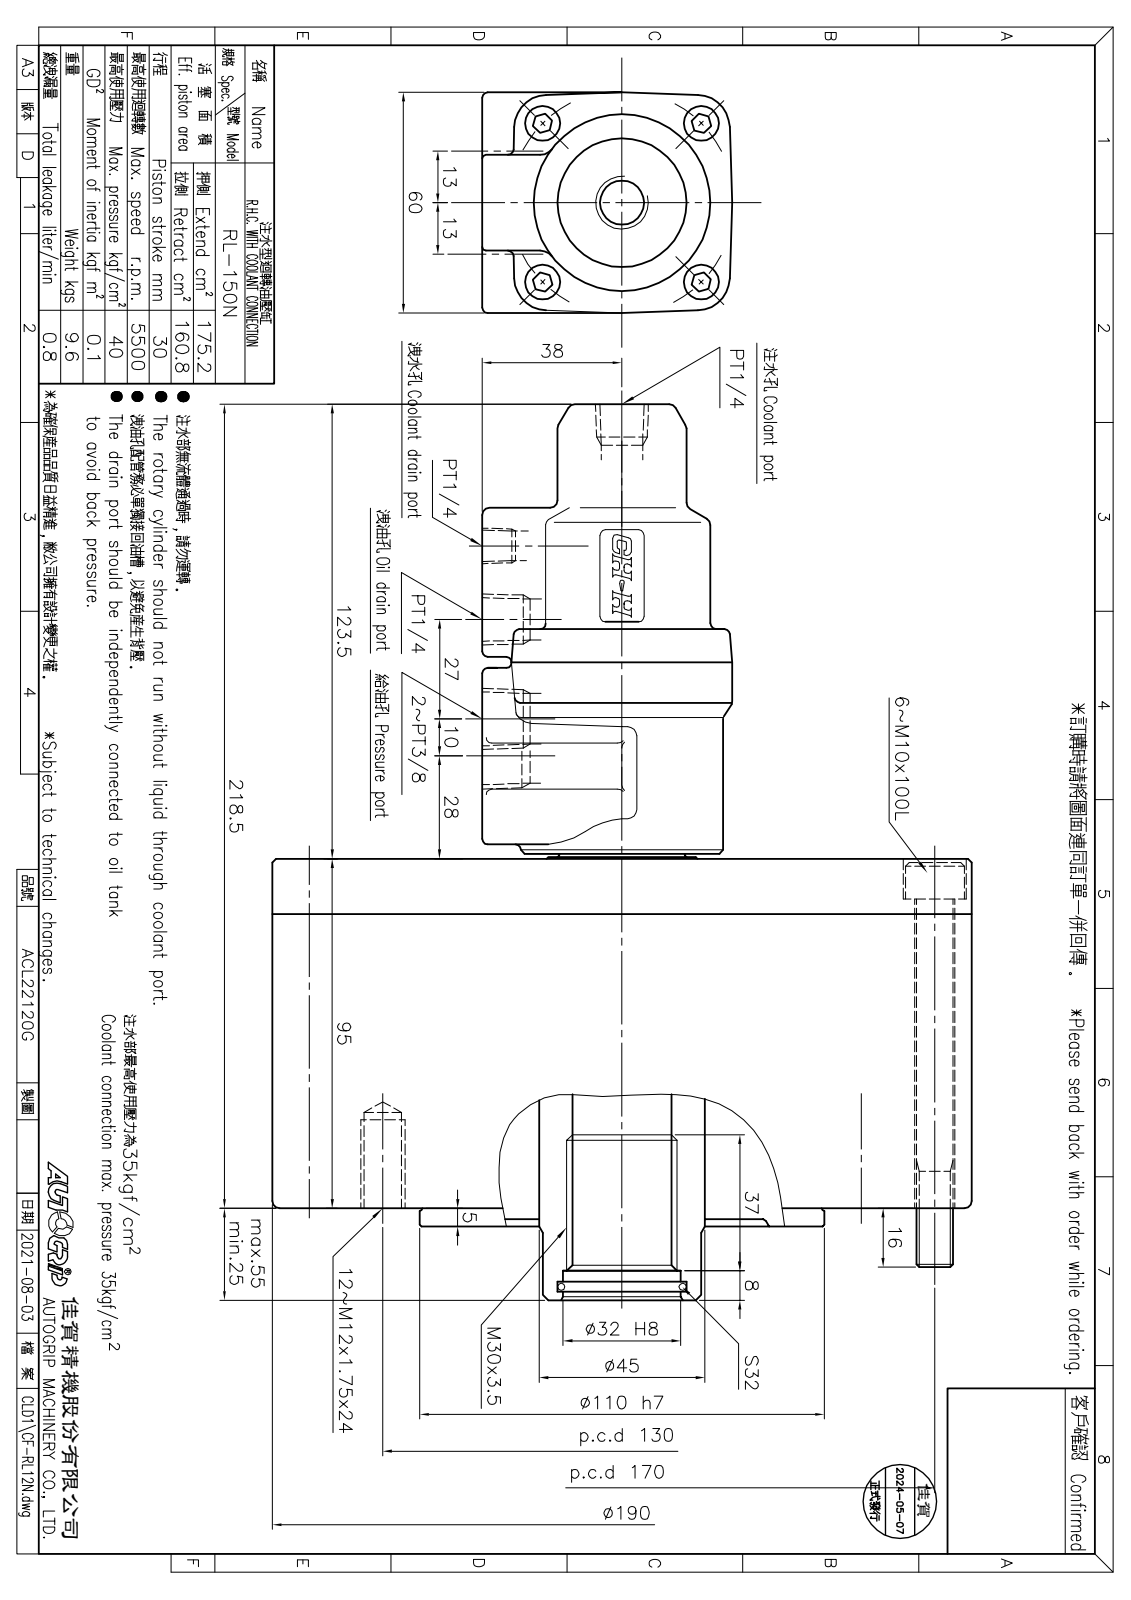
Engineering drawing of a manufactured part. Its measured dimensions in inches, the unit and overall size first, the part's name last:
Units: inches
Overall size (bounding box): 9.587 × 7.48 × 7.48
Round holes (diameter × count): ⌀0.402 ×12, ⌀0.472 ×12, ⌀0.433 ×6, ⌀0.669 ×6, ⌀0.441 ×2, ⌀0.579 ×2, ⌀0.327 ×1, ⌀1.181 ×1, ⌀1.22 ×1, ⌀1.26 ×1, ⌀1.772 ×1
Round bosses / shafts (diameter × count): ⌀7.48 ×1, ⌀5.906 ×1, ⌀4.331 ×1, ⌀2.165 ×1, ⌀1.89 ×1, ⌀1.693 ×1, ⌀1.378 ×1
Partial cylindrical surfaces — rounded edges, fillets, slot ends (radius × count): R0.059 ×24, R0.236 ×4, R0.354 ×4, R0.079 ×3, R0.197 ×2, R0.591 ×2
Main face-to-face distances: 1.181, 0.866, 2.559, 1.378, 0.591, 0.276, 1.693, 2.874, 0.787, 2.362
Hole centre spacings: 2.559, 3.346, 4.433, 5.856, 1.097, 1.325, 2.374, 3.619
Volume: 148.8 in³ · Surface area: 515.9 in²
Bodies: 5 solids, 436 faces (85 planar, 170 cylindrical, 181 other)
Part name (STEP PRODUCT): RL-150活塞; RK-150缸體; RL-150N組合件
STEP written by: SolidWorks 2010 (CONFIG_CONTROL_DESIGN)
